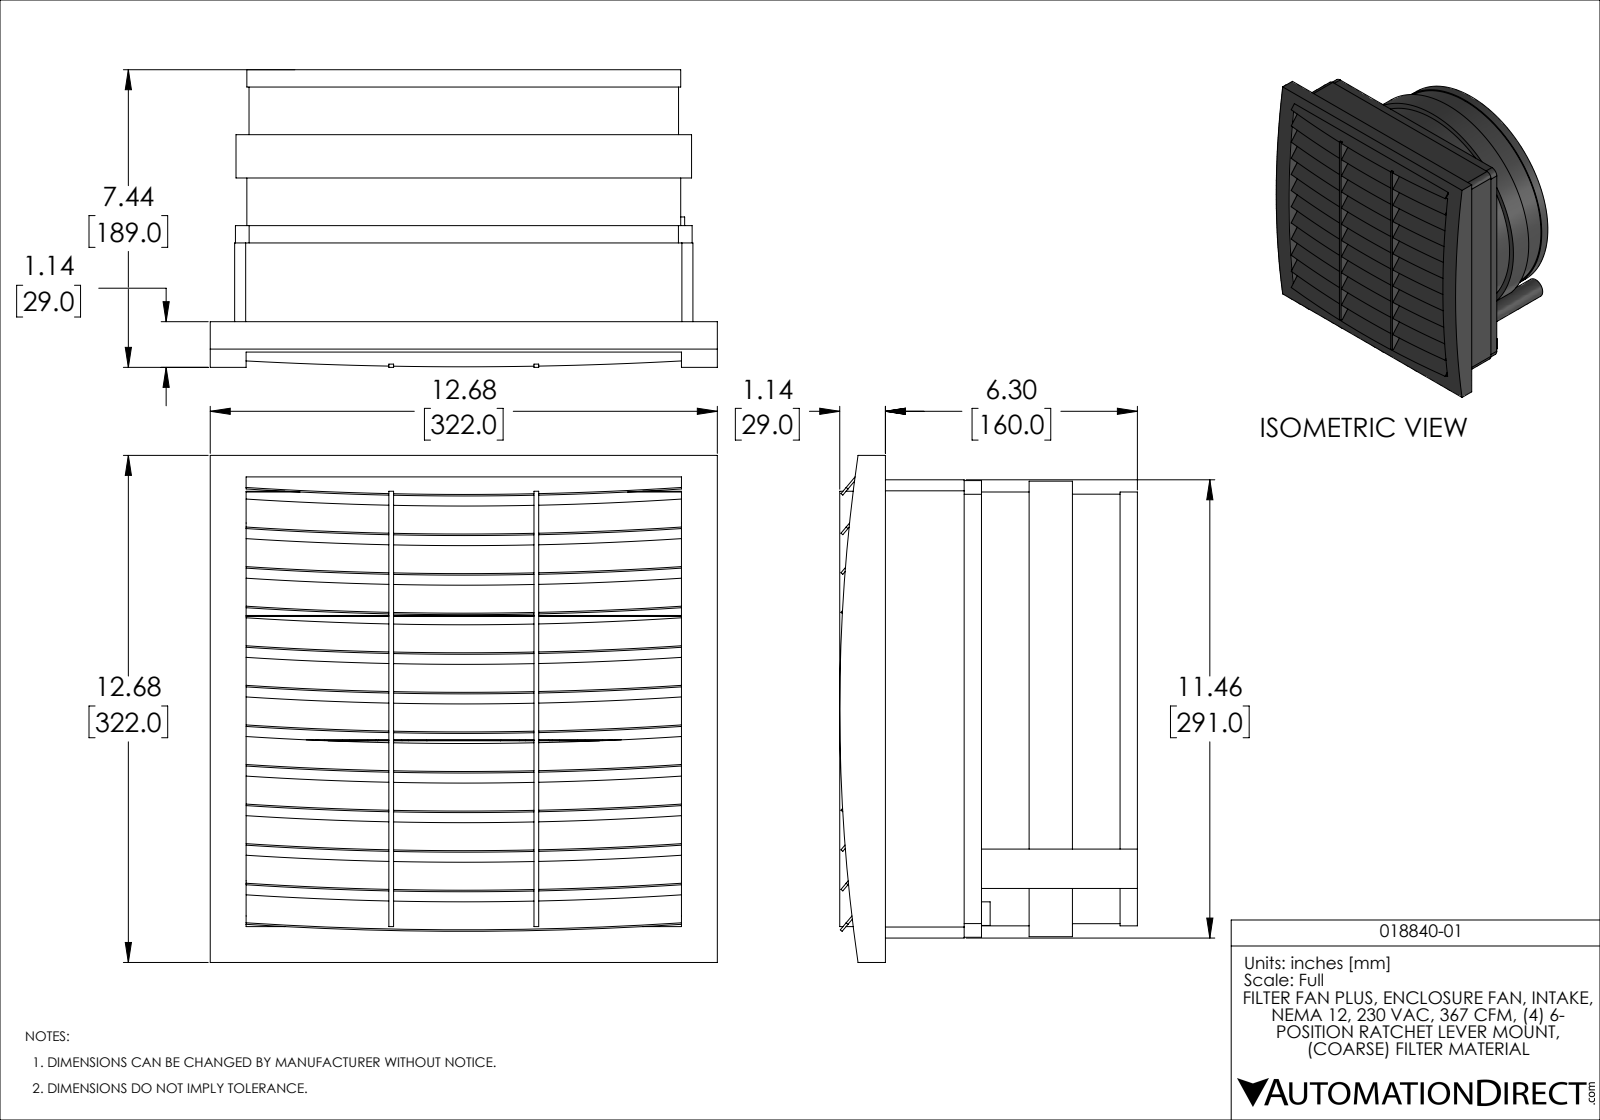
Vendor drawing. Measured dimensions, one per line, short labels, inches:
name: PRODUCT_NAME_1
written by: ACIS (AUTOMOTIVE_DESIGN_CC2)
unit: in
bodies: 1 solid, 916 faces (506 planar, 410 cylindrical, 0 other)
size: 12.677 × 12.677 × 7.441
volume: 283.7 in³; area: 1 629 in²
holes: 1× ⌀3, 1× ⌀3.989, 1× ⌀4.692, 1× ⌀4.979, 1× ⌀5.909, 1× ⌀5.969, 1× ⌀6.958, 1× ⌀7.126, 1× ⌀7.948, 1× ⌀8.344, 1× ⌀9.134, 1× ⌀9.738
bosses: 1× ⌀11.389, 1× ⌀10.846, 1× ⌀10.738, 1× ⌀8.698, 1× ⌀8.341, 1× ⌀7.481, 1× ⌀7.352, 1× ⌀6.362
rounds: 23× R64.96, 7× R4.43, 4× R0.276, 4× R0.343, 1× R1.217, 1× R1.737, 1× R1.915, 1× R44.216
face distances: 0.059, 0.636, 0.27, 1.272, 1.909, 0.541, 2.545, 0.197, 0.811, 3.181
